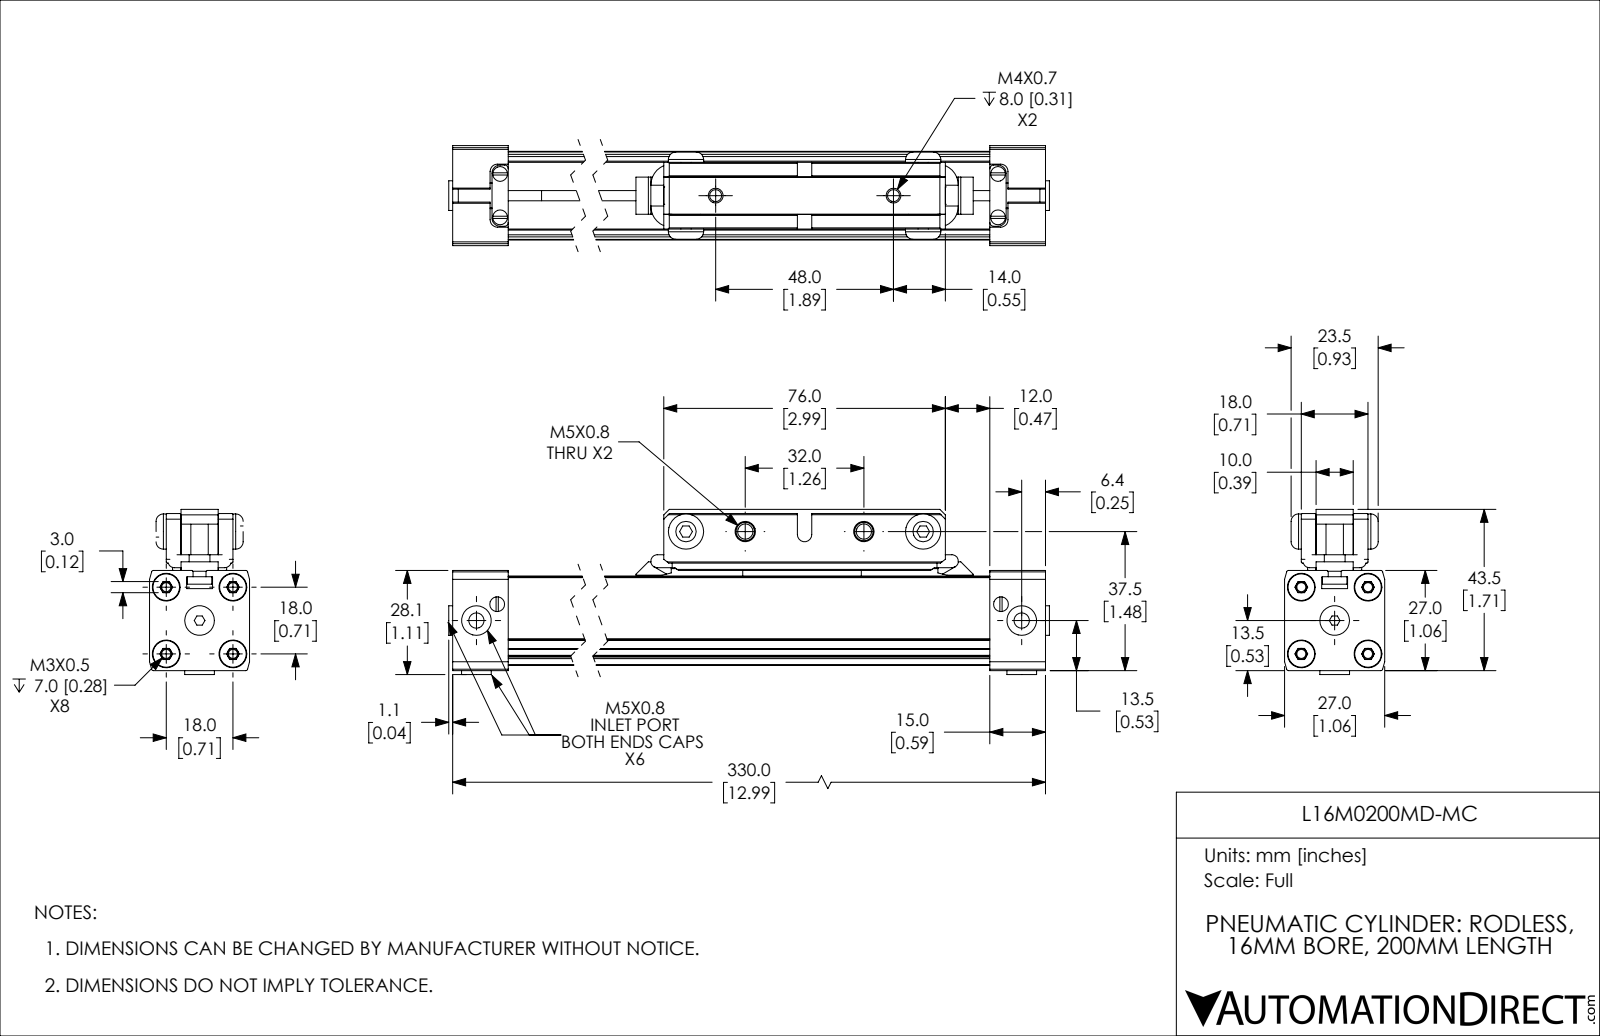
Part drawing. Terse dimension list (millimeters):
name: L16M0200MD-MC_BODY; L16M0200MD-MC_PISTON; L16M0200MD-MC
written by: SolidWorks 2019 (CONFIG_CONTROL_DESIGN)
unit: mm
bodies: 13 solids, 827 faces (435 planar, 284 cylindrical, 108 other)
size: 332.15 × 44.57 × 27
volume: 157 540 mm³; area: 81 799 mm²
holes: 9× ⌀4.13, 6× ⌀4, 5× ⌀8, 4× ⌀2.46, 4× ⌀5.5, 4× ⌀7.5, 2× ⌀3.24, 1× ⌀16.1
bosses: 4× ⌀7.2, 4× ⌀3.5, 3× ⌀5, 3× ⌀3.8, 2× ⌀9.5, 1× ⌀16
rounds: 22× R0.3, 14× R0.5, 8× R0.25, 6× R0.62, 6× R1, 4× R0.2, 4× R0.6, 4× R2
face distances: 23.9, 24, 20.95, 2.95, 1.5, 25.5, 10.05, 3.95, 4, 10.58
hole spacings: 8.67, 12.73, 18, 310.86, 48, 7.12, 11.7, 11.91
